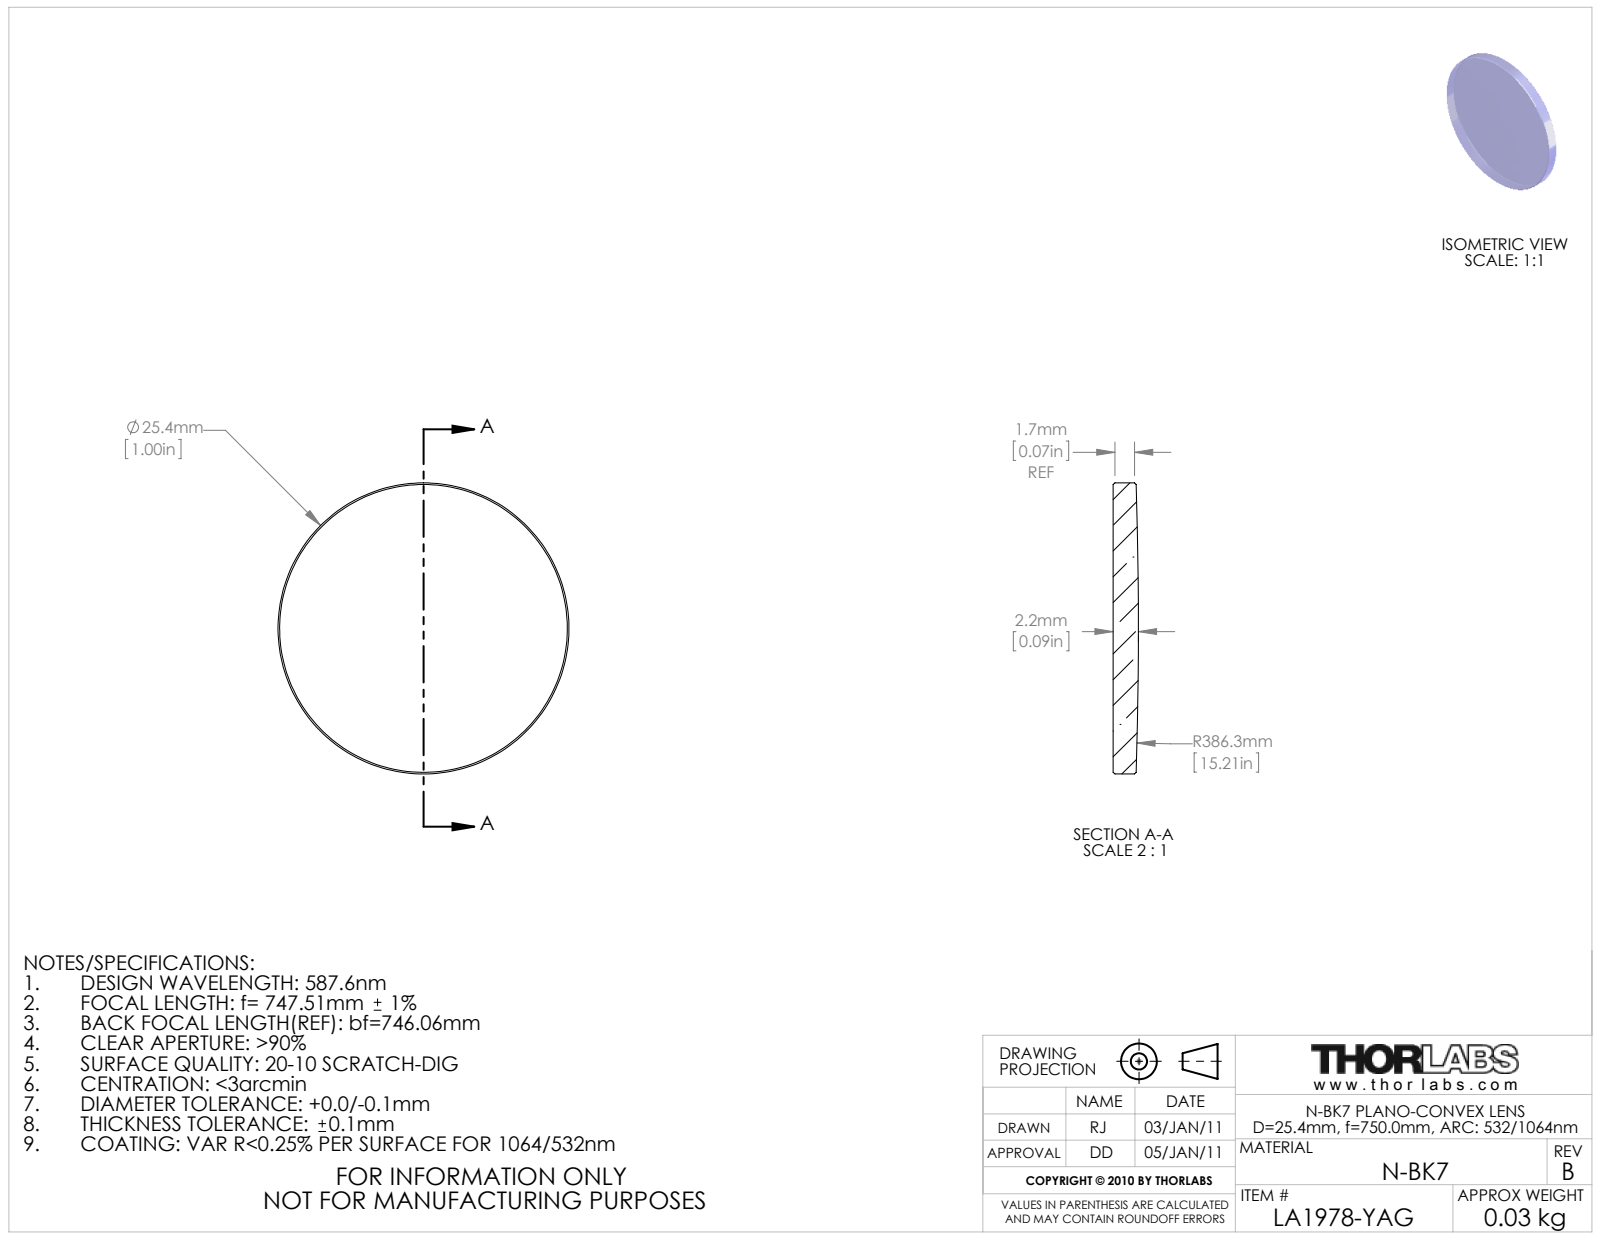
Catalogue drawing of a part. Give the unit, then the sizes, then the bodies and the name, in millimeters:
Units: millimetres
Overall size (bounding box): 25.4 × 25.4 × 2.2
Round bosses / shafts (diameter × count): ⌀25.4 ×1
Bodies: 0 solids, 9 faces (1 planar, 2 cylindrical, 6 other)
Part name (STEP PRODUCT): 21803-E0W
STEP written by: SolidWorks 2011 (AUTOMOTIVE_DESIGN)
